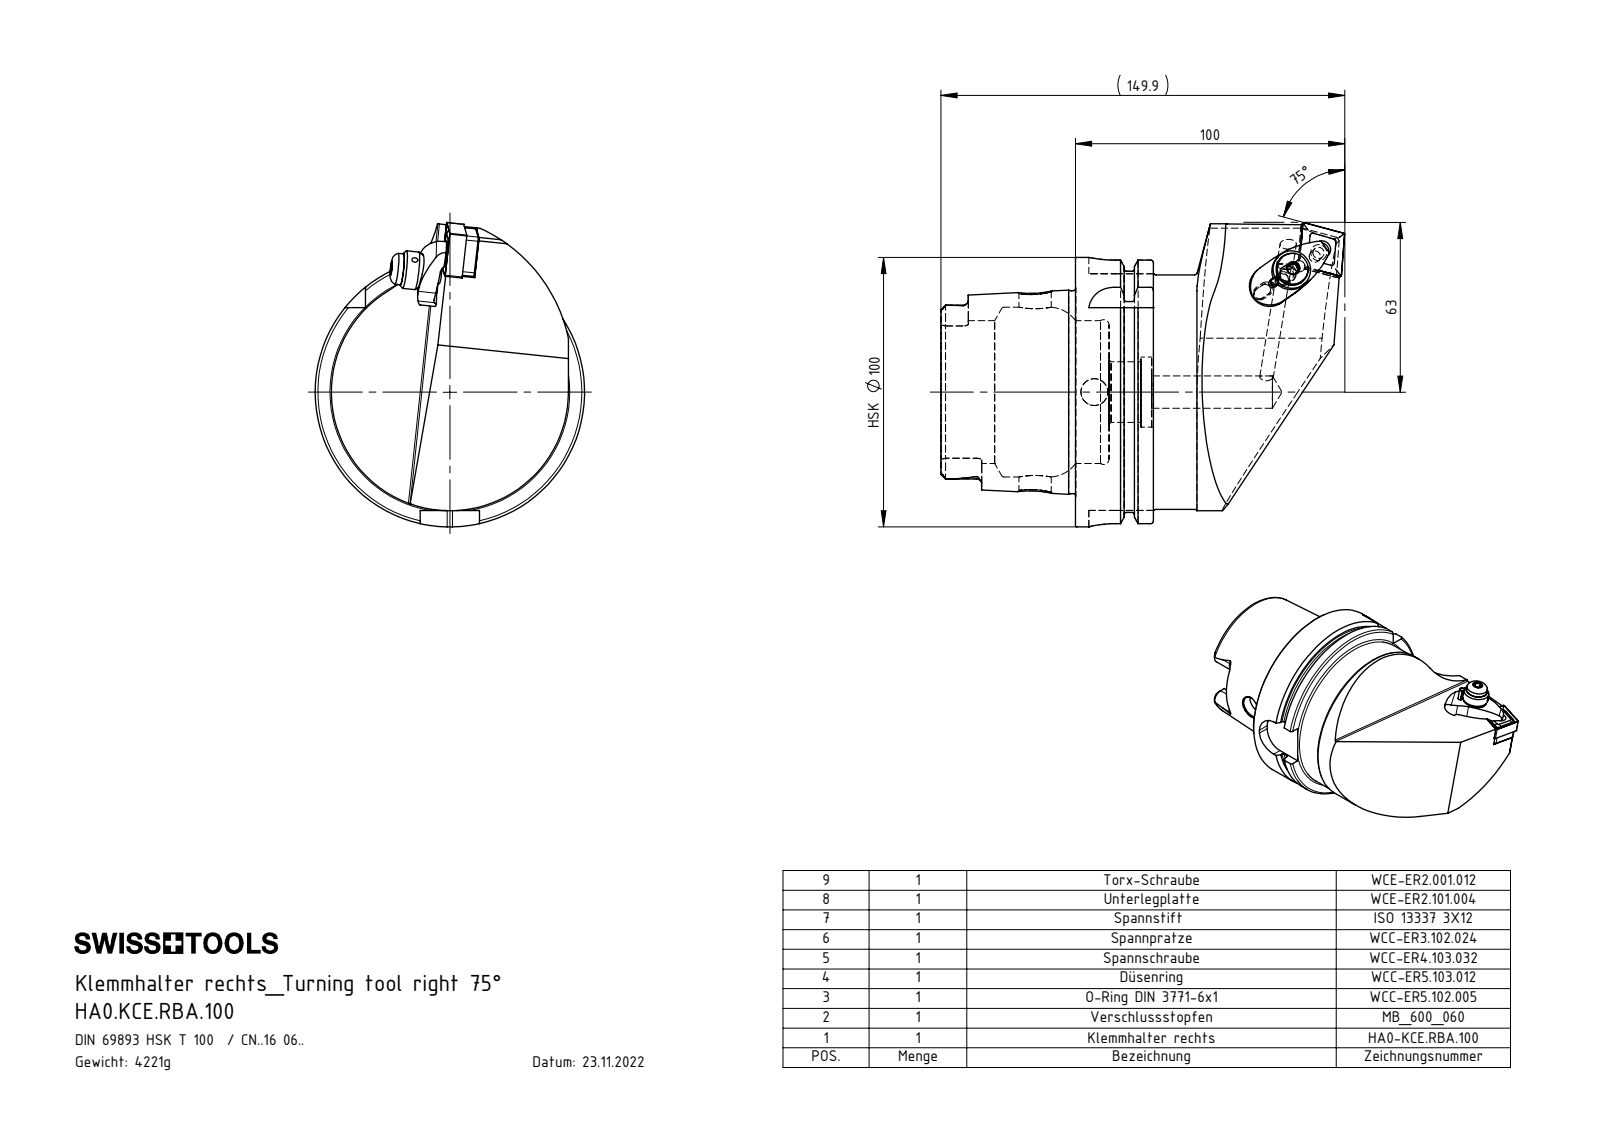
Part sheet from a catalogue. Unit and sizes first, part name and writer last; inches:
Units: inches
Overall size (bounding box): 5.9 × 4.447 × 3.937
Round holes (diameter × count): ⌀0.079 ×3, ⌀0.197 ×3, ⌀0.165 ×2, ⌀0.276 ×2, ⌀0.472 ×2, ⌀0.094 ×1, ⌀0.118 ×1, ⌀0.157 ×1, ⌀0.236 ×1, ⌀0.244 ×1, ⌀0.25 ×1, ⌀0.317 ×1
Round bosses / shafts (diameter × count): ⌀0.236 ×2, ⌀0.118 ×2, ⌀3.937 ×1, ⌀3.62 ×1, ⌀3.425 ×1, ⌀2.963 ×1, ⌀0.551 ×1, ⌀0.453 ×1
Partial cylindrical surfaces — rounded edges, fillets, slot ends (radius × count): R0.018 ×6, R0.075 ×6, R0.059 ×5, R0.016 ×4, R0.031 ×4, R0.394 ×4, R1.575 ×3, R0.031 ×2
Main face-to-face distances: 0.49, 1.14, 0.65, 1.965, 2.455, 3.104, 3.457, 0.026, 3.079, 1.114
Hole centre spacings: 0.315, 0.258, 0.323, 0.572, 0.608, 0.614, 0.929, 0.25
Volume: 32.75 in³ · Surface area: 115.4 in²
Bodies: 11 solids, 467 faces (123 planar, 153 cylindrical, 191 other)
Part name (STEP PRODUCT): WCC-ER5.102.005_A; WCC-ER4.103.032_B; CNMG160604; WCE-ER2.001.012_A (+7 more)
STEP written by: SolidWorks 2017 (AUTOMOTIVE_DESIGN)
